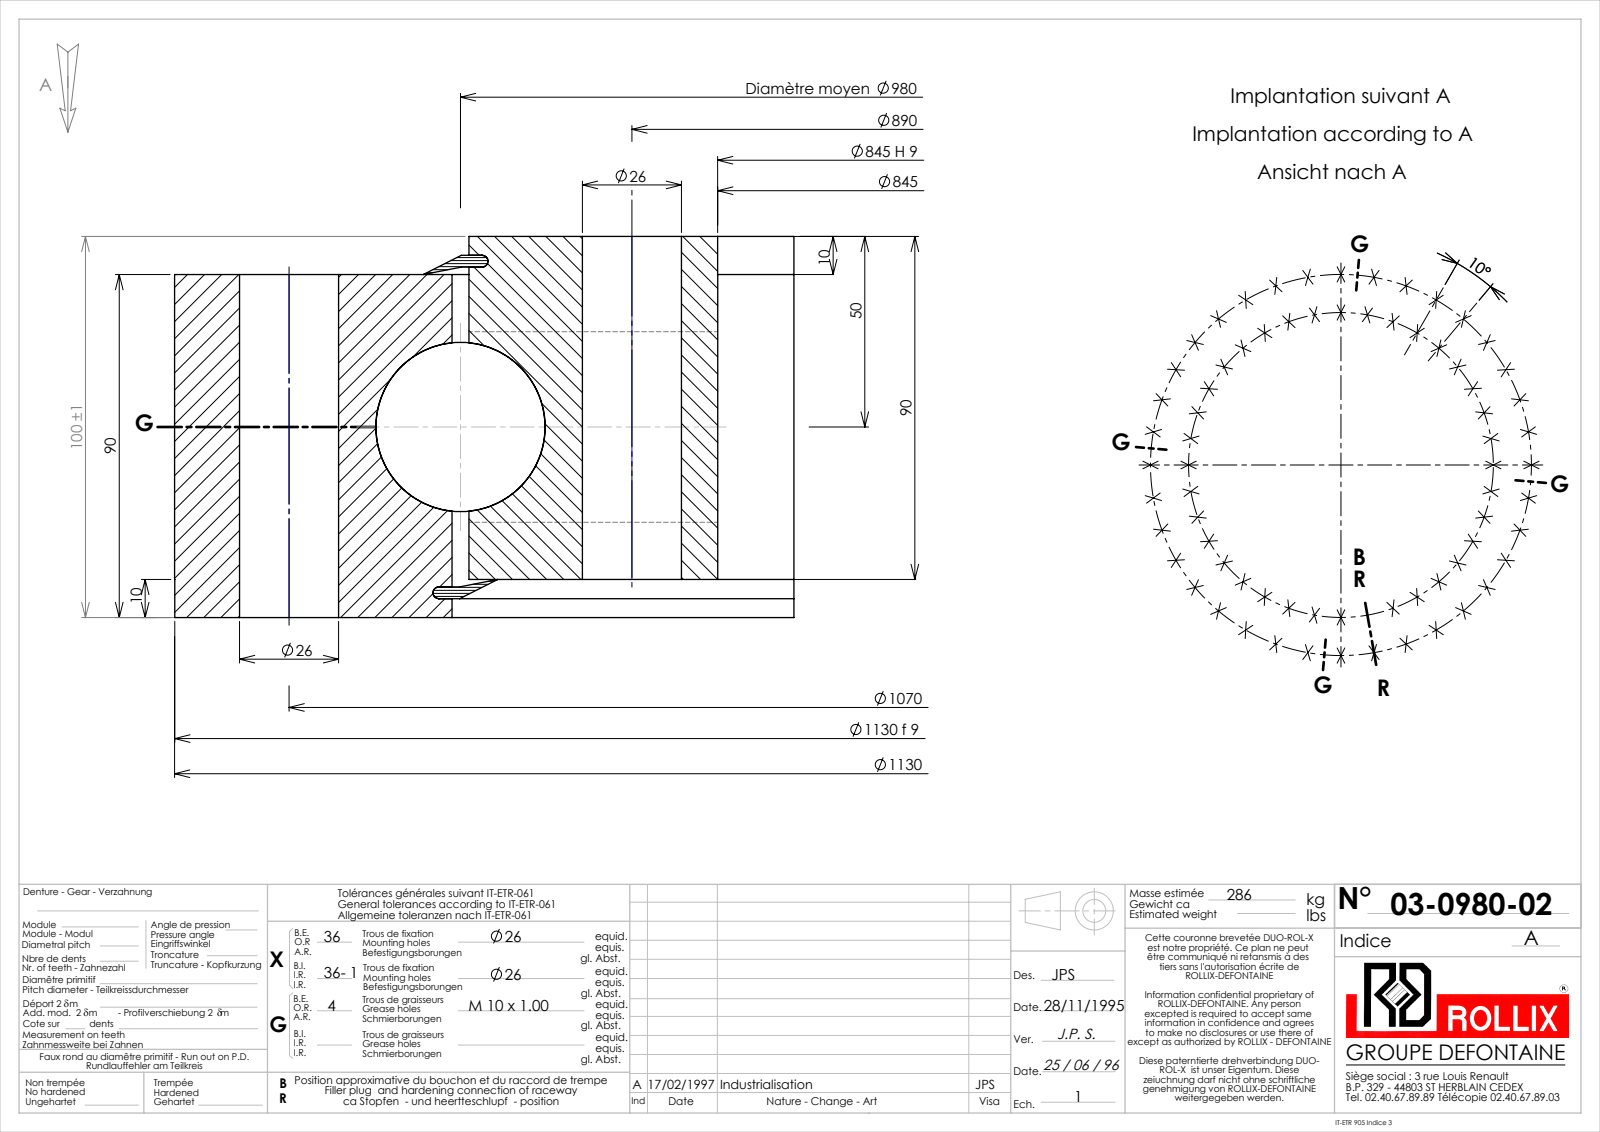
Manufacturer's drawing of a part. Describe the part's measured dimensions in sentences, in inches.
The part is named "03-0980-02". Its 3-D file was written by "SolidWorks 2016 (CONFIG_CONTROL_DESIGN)". It is 5 solids with 214 faces: 14 planar, 172 cylindrical and 28 other. Overall it measures 44.492 by 44.492 by 3.937 inches. Its volume is 1 900 cubic inches and its surface area 4 413 square inches. Round holes: 72 of diameter 1.024, 4 of diameter 0.354, 1 of diameter 33.266, 1 of diameter 33.268, 1 of diameter 38.757, 1 of diameter 38.758. Round bosses or shafts: 1 of diameter 44.492, 1 of diameter 44.488, 1 of diameter 38.407. The main face-to-face distances are 3.543, 0.394, 3.15, 3.937, 0.195, 3.742, 0.199, 3.348, 0.317, 3.62. The hole center spacings are 3.054, 9.069, 17.52, 26.842, 30.345, 33.845, 34.507, 34.906.
